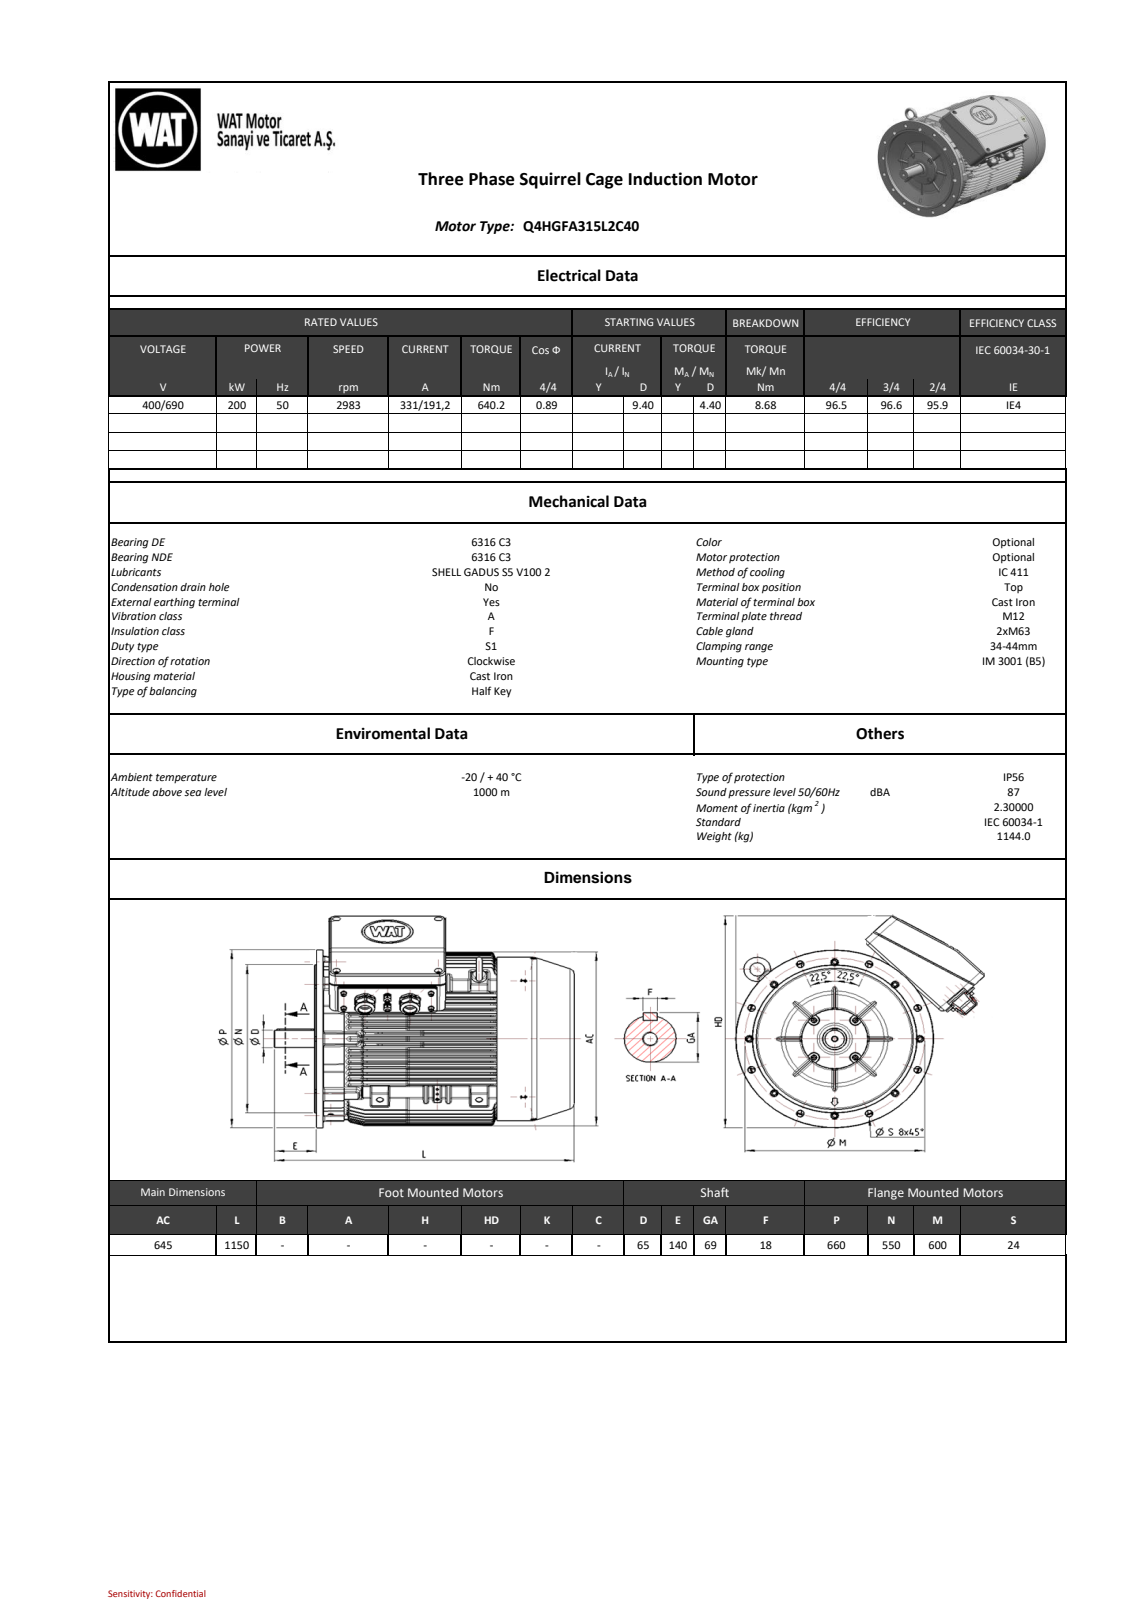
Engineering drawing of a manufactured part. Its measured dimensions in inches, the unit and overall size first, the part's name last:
Units: inches
Overall size (bounding box): 45.276 × 32.645 × 30.933
Round holes (diameter × count): ⌀0.945 ×8, ⌀1.024 ×8, ⌀0.787 ×5, ⌀0.315 ×4, ⌀0.335 ×4, ⌀0.354 ×4, ⌀0.866 ×4, ⌀0.472 ×2, ⌀0.591 ×2, ⌀0.709 ×2, ⌀0.827 ×2, ⌀1.732 ×2
Round bosses / shafts (diameter × count): ⌀0.63 ×8, ⌀0.787 ×7, ⌀0.394 ×4, ⌀2.551 ×2, ⌀1.969 ×2, ⌀25.984 ×1, ⌀23.898 ×1, ⌀22.244 ×1
Partial cylindrical surfaces — rounded edges, fillets, slot ends (radius × count): R0.236 ×472, R0.118 ×154, R0.082 ×66, R0.103 ×61, R0.031 ×32, R0.394 ×26, R0.016 ×19, R0.059 ×14
Main face-to-face distances: 4.606, 0.815, 12.014, 1.634, 11.195, 0.819, 10.38, 9.546, 3.283, 2.457
Hole centre spacings: 19.153, 4.53, 4.531, 8.588, 11.811, 12.805, 12.806, 16.703
Bodies: 0 solids, 5794 faces (2589 planar, 1181 cylindrical, 2024 other)
Part name (STEP PRODUCT): 26009910674F4pqf
STEP written by: SIEMENS PLM Software NX 11.0 (AUTOMOTIVE_DESIGN)
